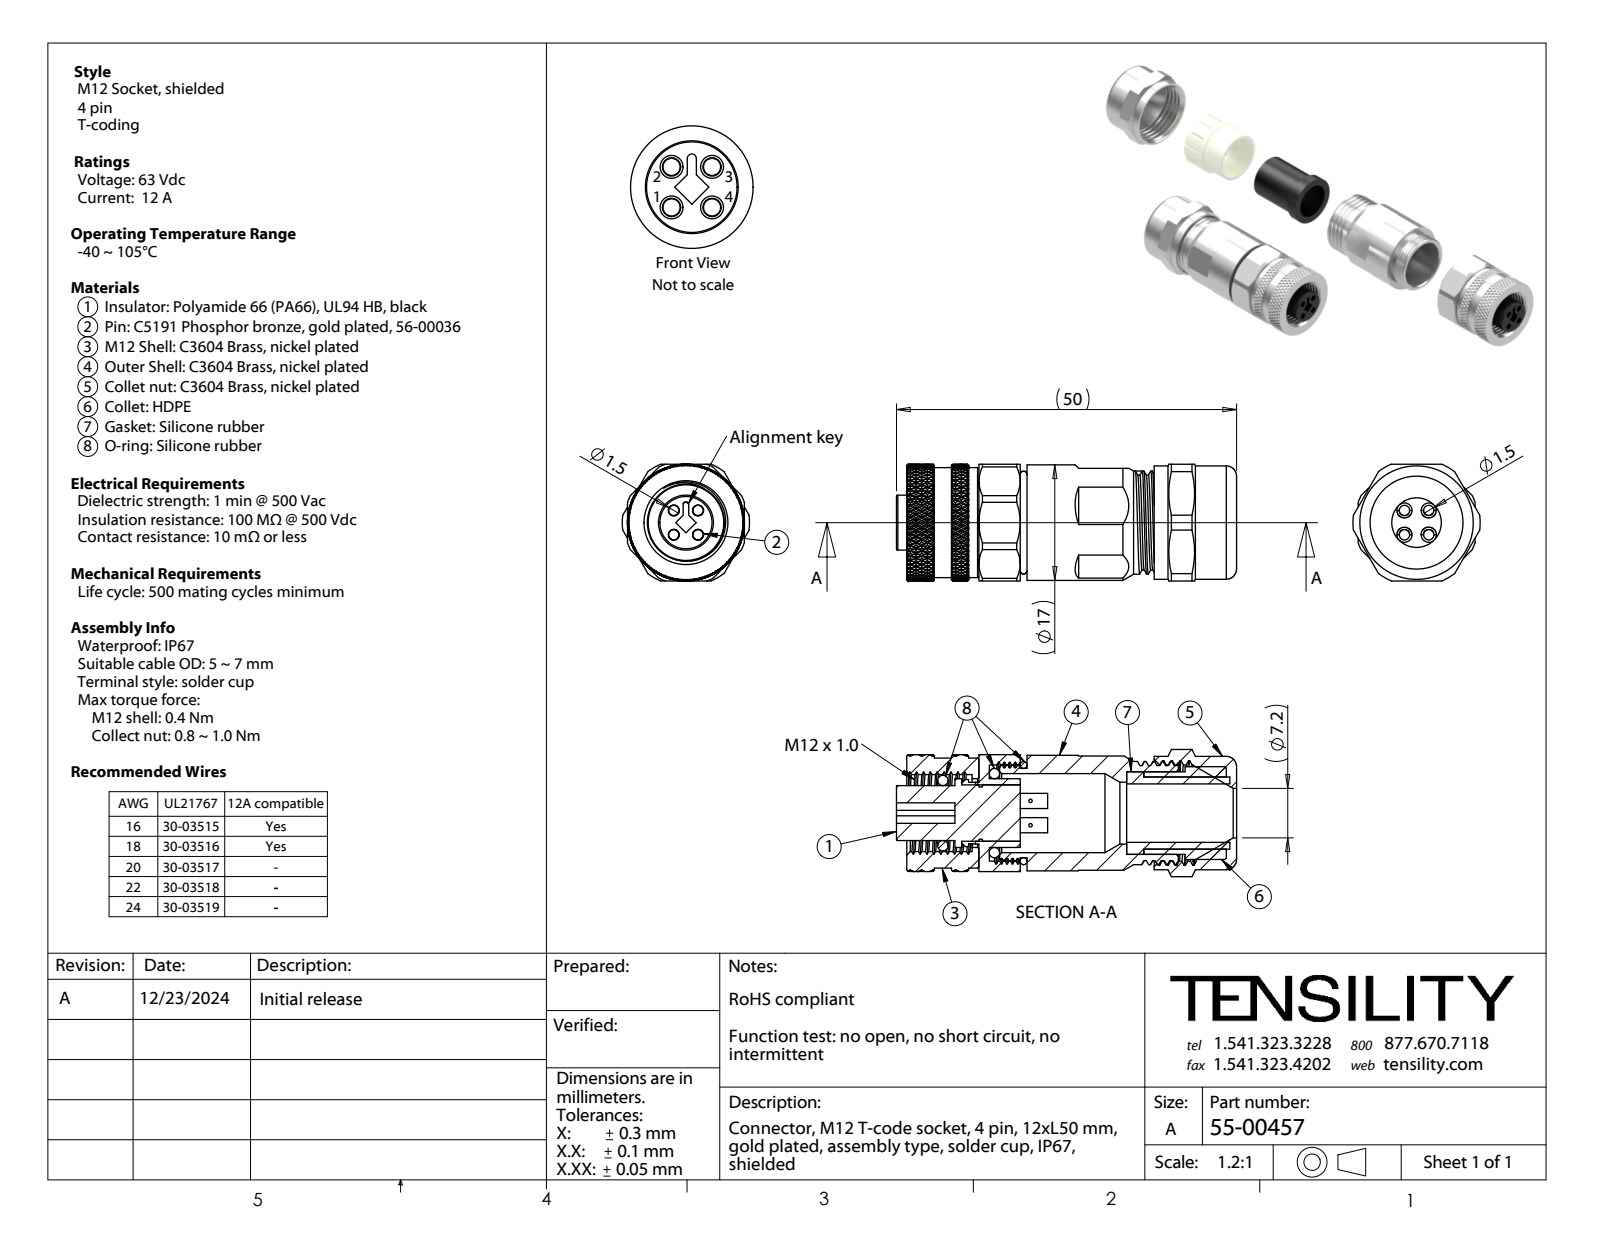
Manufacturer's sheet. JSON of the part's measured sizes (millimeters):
{"part_name": "55-00457-01; 55-00457-04; 55-00457-10; 55-00457-11 (+8 more)", "step_written_by": "SolidWorks 2021 (CONFIG_CONTROL_DESIGN)", "units": "millimeters", "bodies": {"solids": 14, "faces": 524, "planar": 189, "cylindrical": 199, "other": 136}, "overall_size": [49.5, 18.5, 17], "volume_mm3": 7430, "surface_area_mm2": 11490, "round_holes": [[1.5, 4], [1.6, 4], [0.5, 2], [7.2, 1], [7.6, 1], [8.2, 1], [8.5, 1], [9, 1], [10.5, 1], [11.2, 1], [11.5, 1], [14, 1]], "round_bosses_or_shafts": [[2.2, 4], [17, 1], [16.8, 1], [16.5, 1], [16, 1], [15, 1], [13.5, 1], [13, 1]], "partial_cylinders_radius": [[1.86, 2], [0.4, 1], [9, 1], [9.25, 1]], "face_to_face_distances": [17, 1.5, 1, 6, 10.5, 7, 12, 36, 37.5, 31.5], "hole_center_spacings": [3.54, 2.5, 5.01]}
